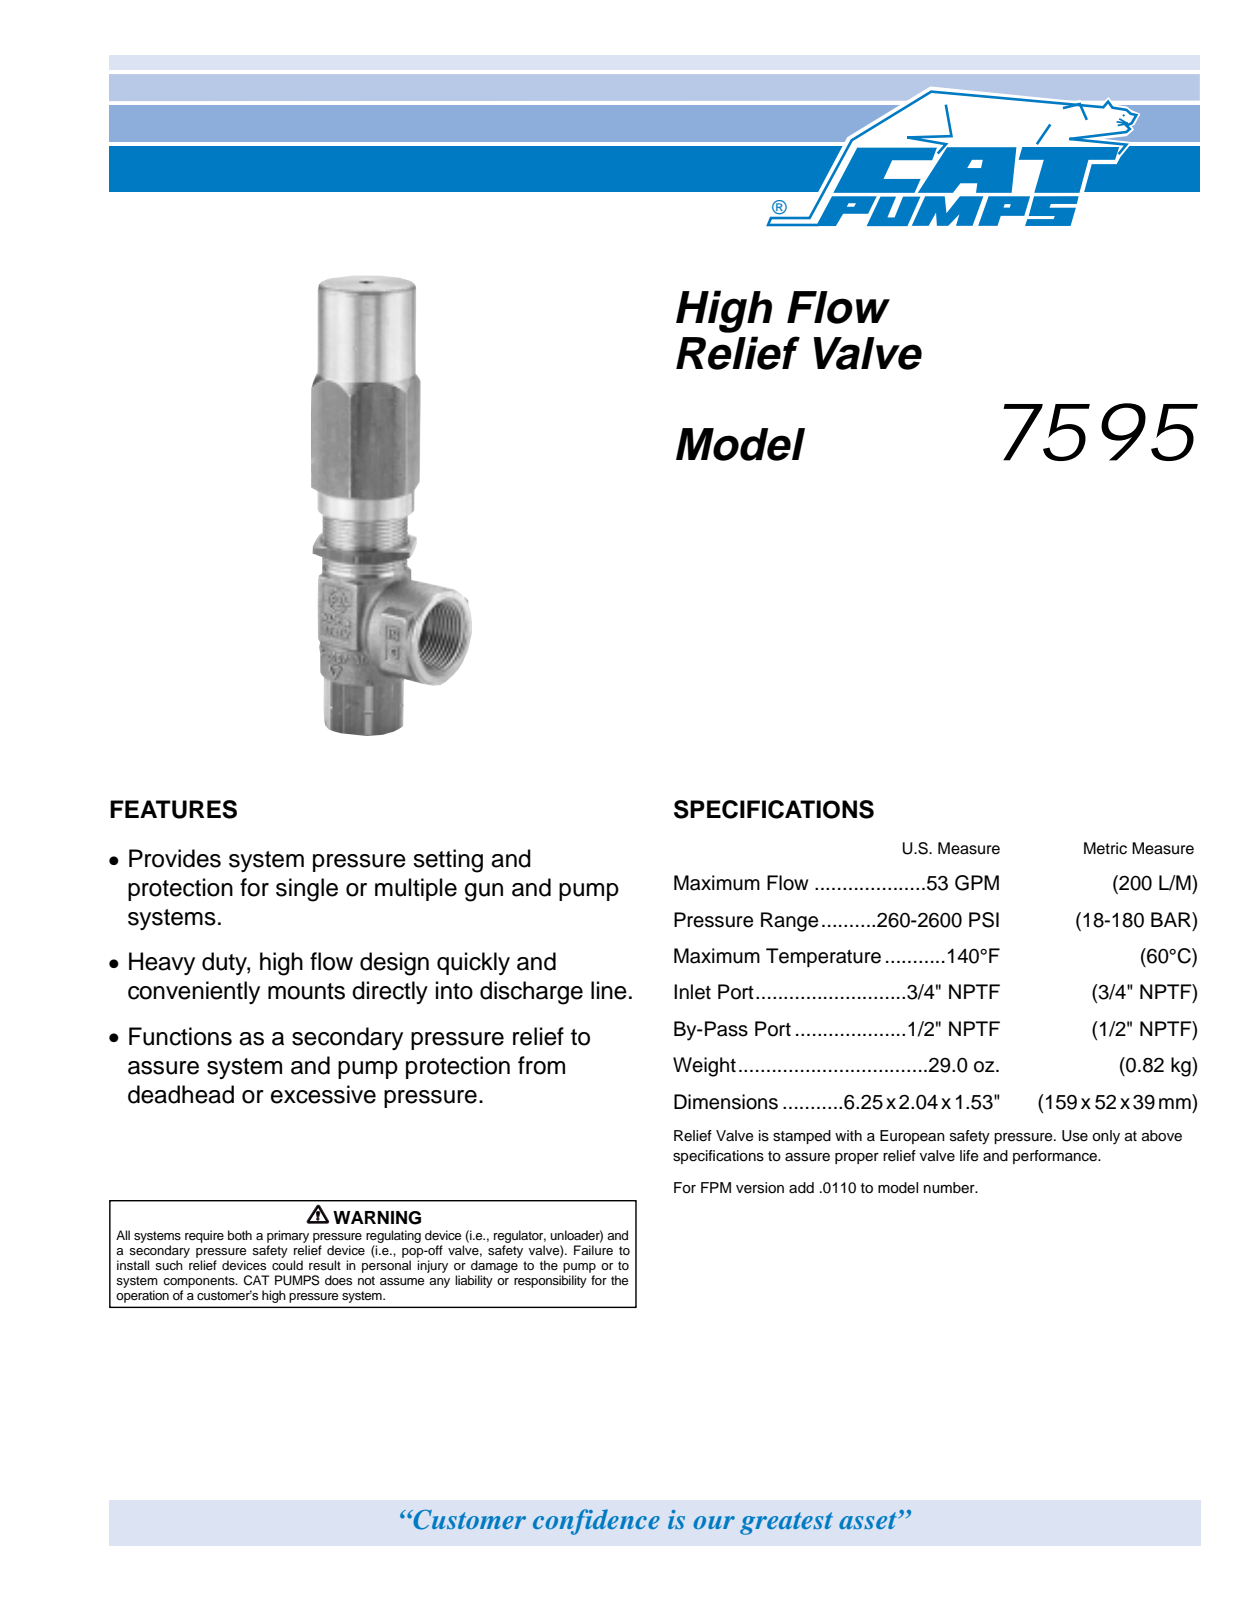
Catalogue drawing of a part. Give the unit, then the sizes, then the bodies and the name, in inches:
Units: inches
Overall size (bounding box): 6.22 × 2.168 × 1.37
Round holes (diameter × count): ⌀0.703 ×1, ⌀0.906 ×1
Round bosses / shafts (diameter × count): ⌀1.36 ×1, ⌀1.33 ×1, ⌀1.2 ×1, ⌀1.175 ×1
Partial cylindrical surfaces — rounded edges, fillets, slot ends (radius × count): R0.02 ×40
Main face-to-face distances: 1.33, 0.135, 1.195, 1.06, 0.065, 1.265, 0.07, 1.13, 1.215, 1.2
Volume: 8.11 in³ · Surface area: 37.7 in²
Bodies: 1 solid, 278 faces (71 planar, 65 cylindrical, 142 other)
Part name (STEP PRODUCT): 7595
STEP written by: SolidWorks 2010 (AUTOMOTIVE_DESIGN)
